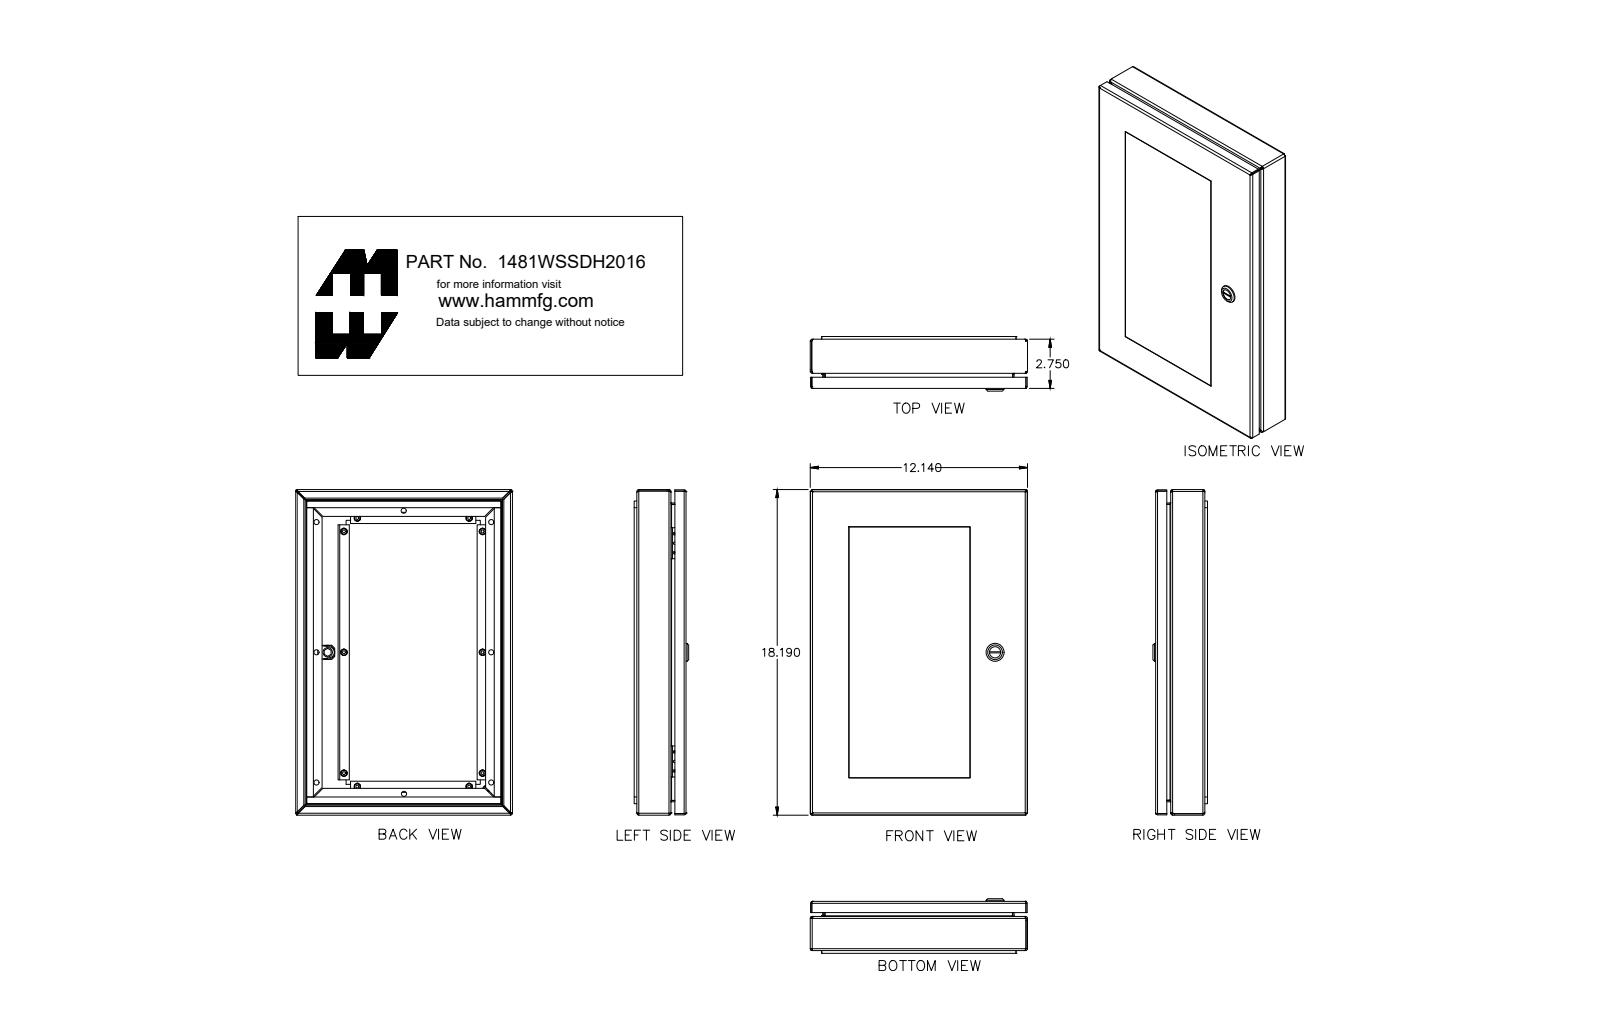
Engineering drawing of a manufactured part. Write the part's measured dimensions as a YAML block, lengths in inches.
part_name: "1481WSSDH2016_Default"
step_written_by: "SolidWorks 2019 (CONFIG_CONTROL_DESIGN)"
units: inches
bodies: {solids: 42, faces: 999, planar: 541, cylindrical: 282, other: 176}
overall_size: [18.19, 12.14, 2.91]
volume: 59.58
surface_area: 1210
round_holes:
  - {diameter: 0.13, count: 10}
  - {diameter: 0.281, count: 8}
  - {diameter: 0.136, count: 2}
  - {diameter: 0.197, count: 1}
  - {diameter: 0.24, count: 1}
  - {diameter: 0.242, count: 1}
  - {diameter: 0.387, count: 1}
  - {diameter: 0.5, count: 1}
  - {diameter: 0.63, count: 1}
  - {diameter: 0.768, count: 1}
round_bosses_or_shafts:
  - {diameter: 0.368, count: 10}
  - {diameter: 0.226, count: 10}
  - {diameter: 0.164, count: 10}
  - {diameter: 1.1, count: 1}
  - {diameter: 0.785, count: 1}
  - {diameter: 0.625, count: 1}
  - {diameter: 0.525, count: 1}
  - {diameter: 0.477, count: 1}
partial_cylinders:
  - {radius: 0.036, count: 28}
  - {radius: 0.108, count: 28}
  - {radius: 0.101, count: 20}
  - {radius: 0.016, count: 4}
  - {radius: 0.088, count: 4}
  - {radius: 0.125, count: 2}
  - {radius: 0.021, count: 1}
  - {radius: 0.029, count: 1}
face_to_face_distances: [0.072, 0.25, 0.178, 2.578, 0.842, 1.736, 2.328, 12.068, 0.592, 2.65]
hole_center_spacings: [4.923, 6.75, 7.04, 10.278, 15.946, 7.75, 9.764, 1.06]
